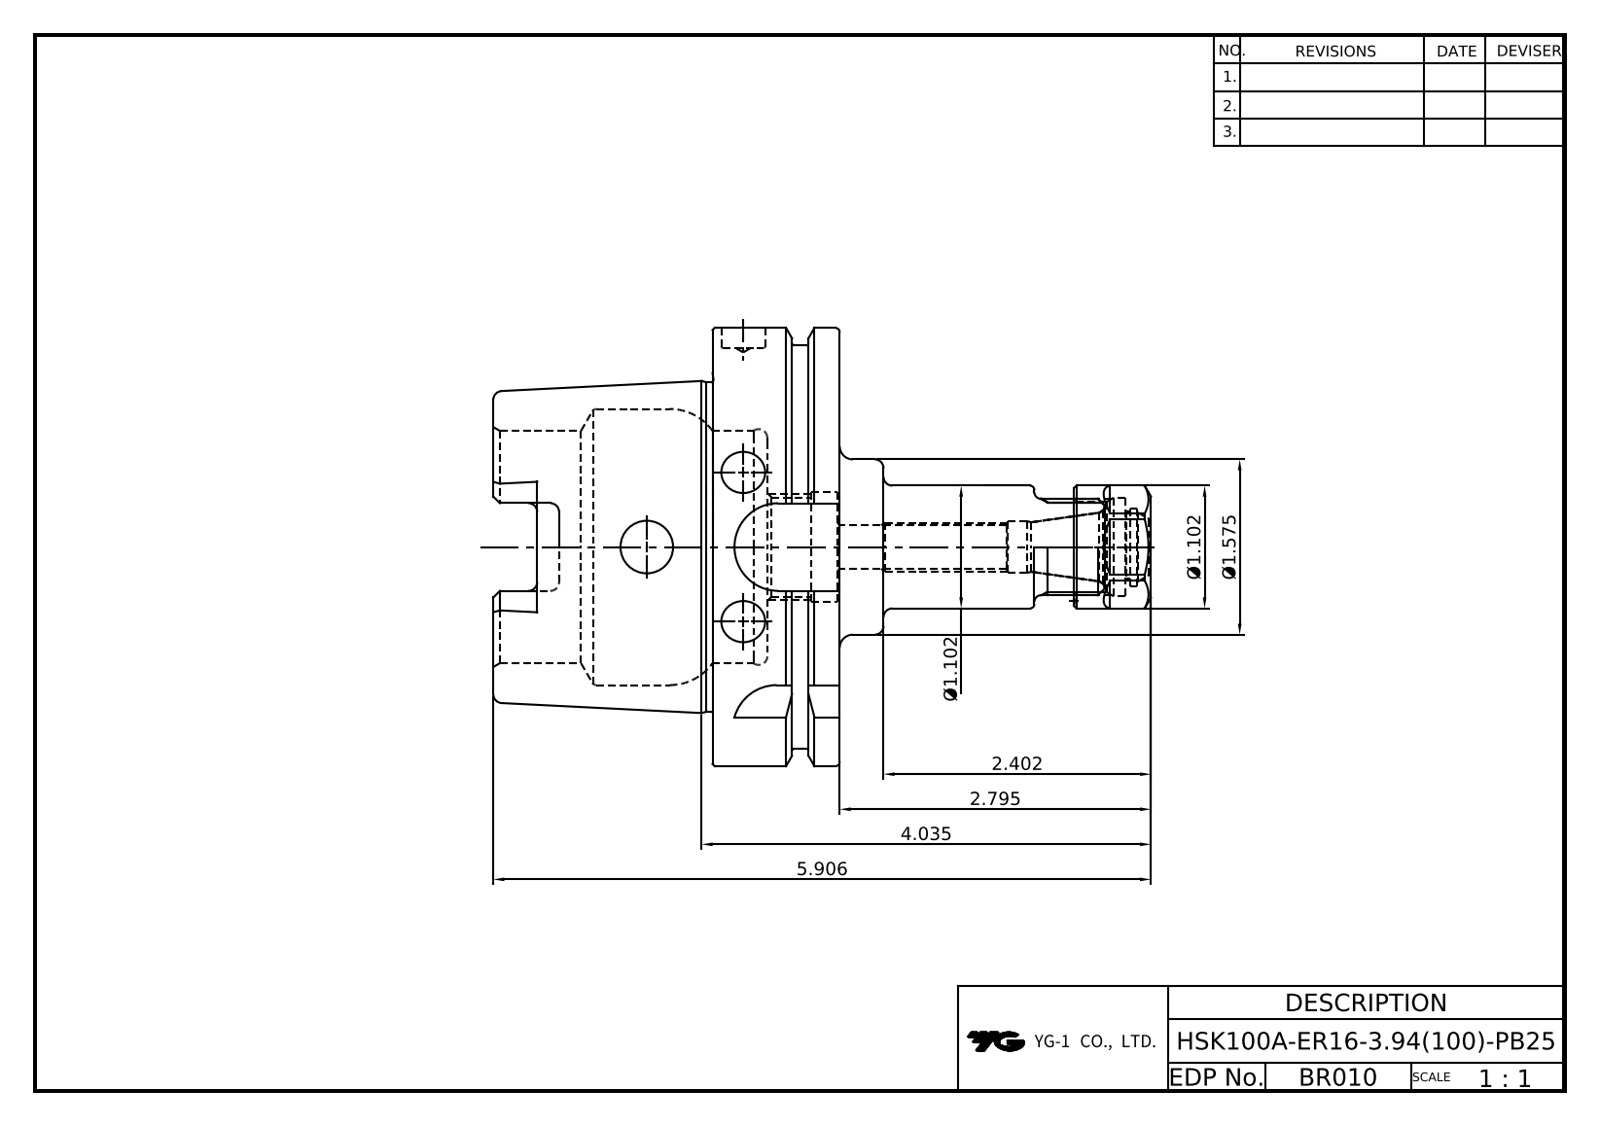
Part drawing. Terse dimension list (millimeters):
name: LO-HSK100A-ER16-3.94; ER16NUT
written by: Autodesk Inventor 2025 (AUTOMOTIVE_DESIGN)
unit: mm
bodies: 2 solids, 154 faces (58 planar, 44 cylindrical, 52 other)
size: 150 × 100 × 100
volume: 293 381 mm³; area: 60 553 mm²
holes: 1× ⌀1, 1× ⌀9.4, 1× ⌀10, 1× ⌀11.8, 1× ⌀12, 1× ⌀12.8, 1× ⌀17.7, 1× ⌀20.6, 1× ⌀22.38, 1× ⌀22.5, 1× ⌀25, 1× ⌀53
bosses: 1× ⌀100, 1× ⌀92, 1× ⌀75.41, 1× ⌀40, 1× ⌀28, 1× ⌀22
rounds: 6× R2, 4× R4.88, 4× R10, 2× R7.7
face distances: 29, 12.5, 16.5, 79, 62.5, 50, 10, 16, 88, 78.5
hole spacings: 12
